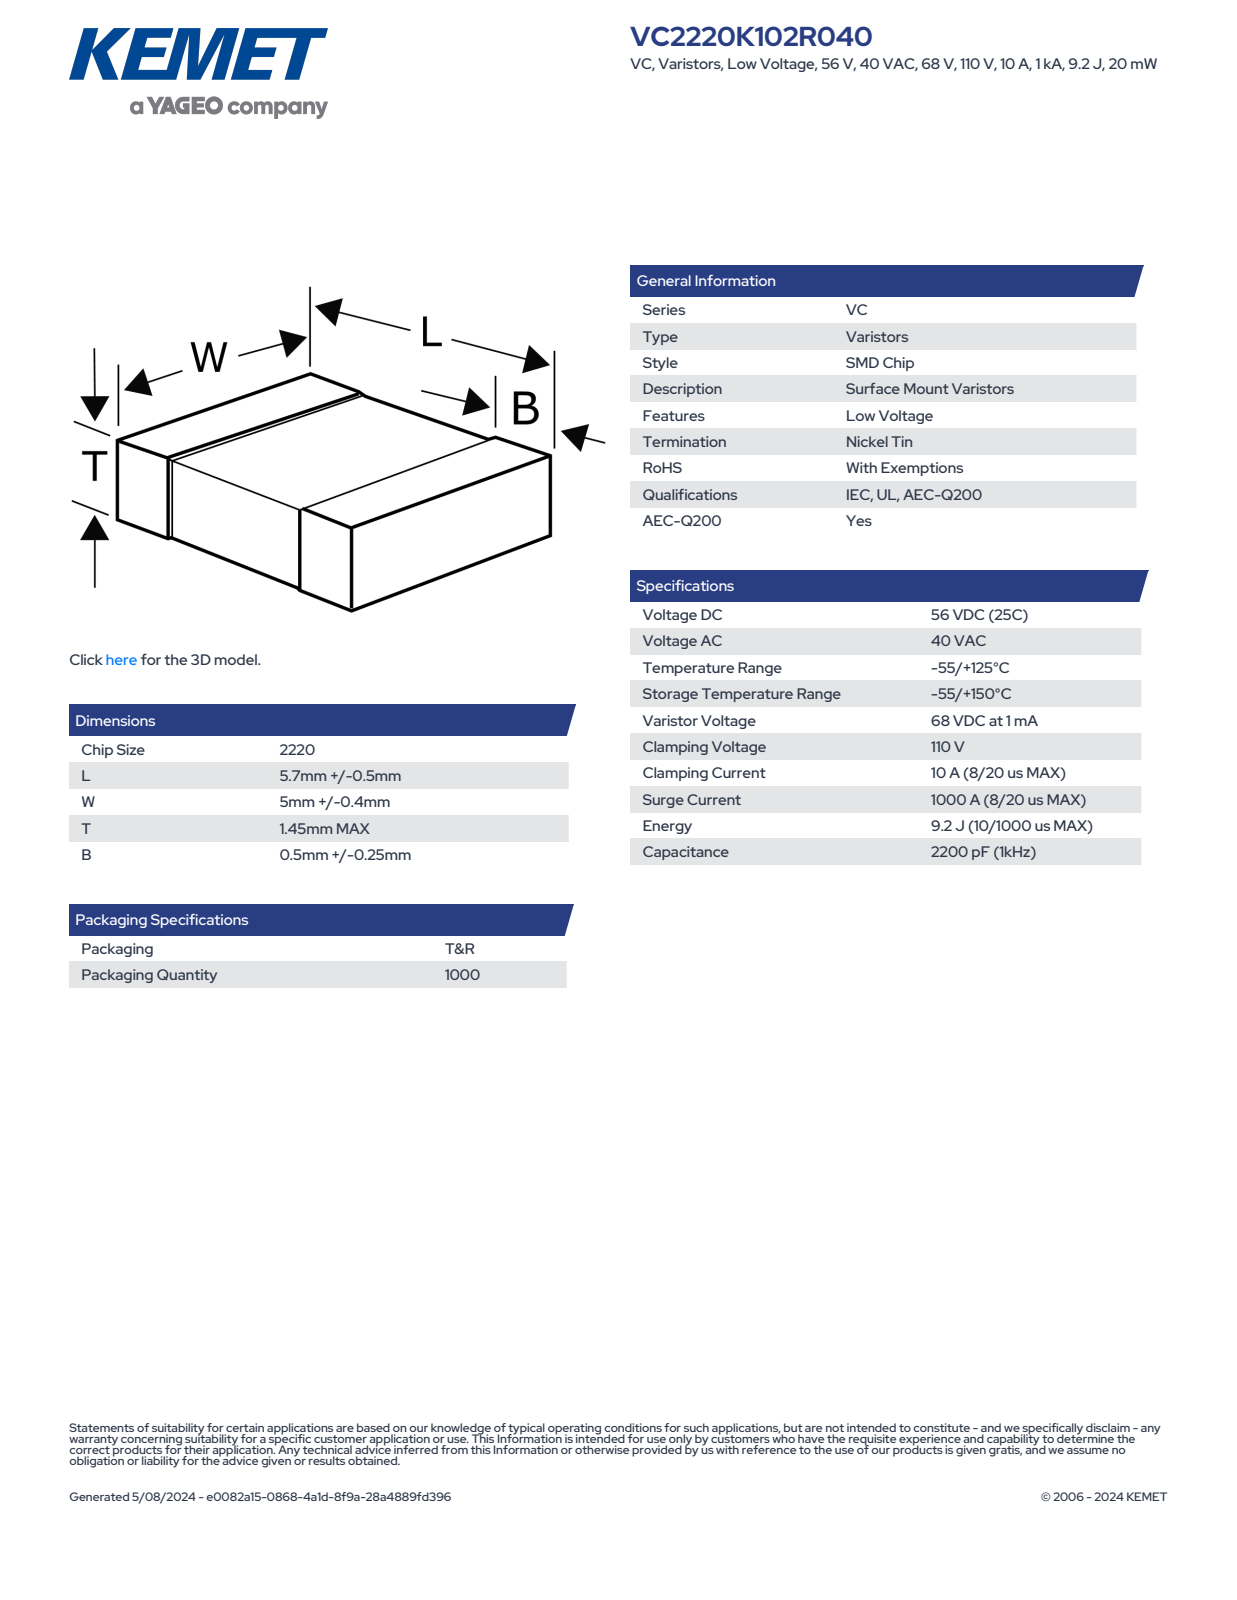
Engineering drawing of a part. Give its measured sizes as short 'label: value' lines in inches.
name: VS_SMD_2220_L6.20W5.4T1.45B0.75
written by: SolidWorks 2014 (AUTOMOTIVE_DESIGN)
unit: in
bodies: 4 solids, 125 faces (71 planar, 38 cylindrical, 16 other)
size: 0.244 × 0.213 × 0.057
volume: 0.003 in³; area: 0.15 in²
rounds: 24× R0.004
face distances: 0.048, 0.053, 0.244, 0.057, 0.204, 0.208, 0.213, 0.112, 0.132, 0.031
